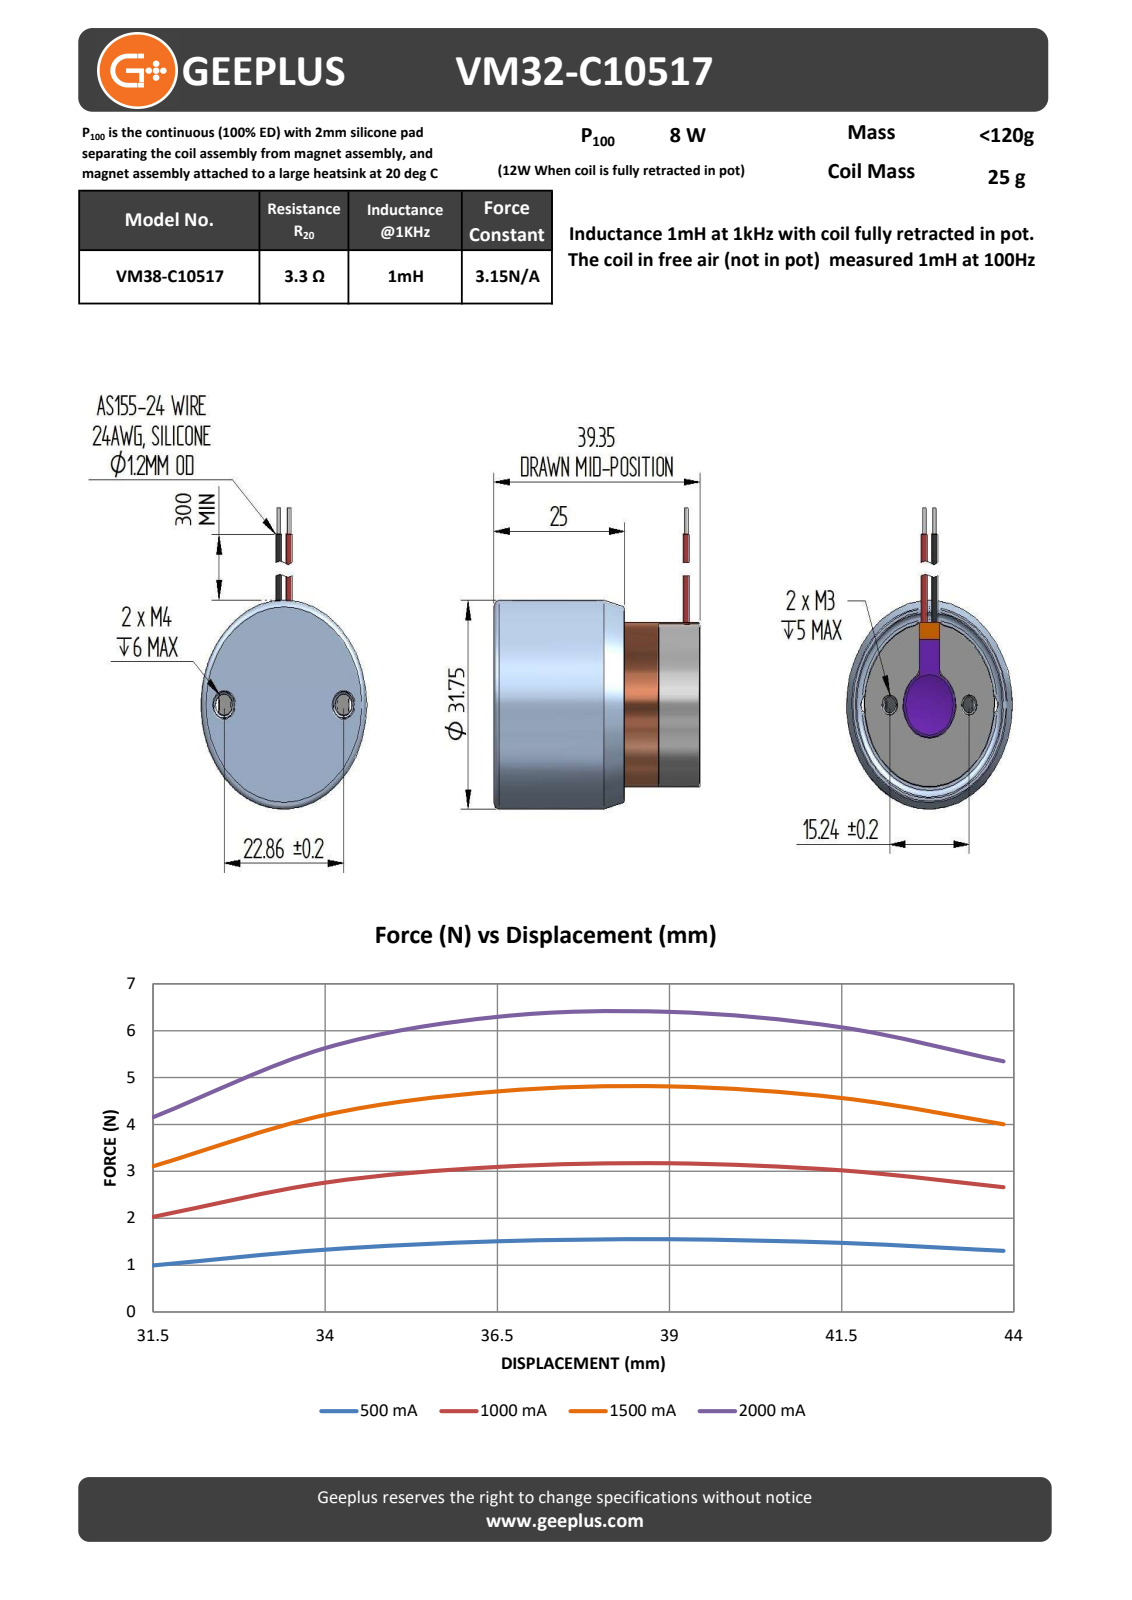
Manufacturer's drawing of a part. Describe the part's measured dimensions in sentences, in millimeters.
The part is named "01-1423; 02-1438; 81-1412; 84-1111 (+8 more)". Its 3-D file was written by "Solid Edge (AUTOMOTIVE_DESIGN)". It is 9 solids with 160 faces: 79 planar, 47 cylindrical and 34 other. Overall it measures 337.28 by 39.35 by 31.75 millimeters. Its volume is 18 259 cubic millimeters and its surface area 17 086 square millimeters. Round holes: 2 of diameter 1, 2 of diameter 2.46, 2 of diameter 3.24, 1 of diameter 10.2, 1 of diameter 11, 1 of diameter 16.1, 1 of diameter 19.4, 1 of diameter 20.4, 1 of diameter 28. Round bosses or shafts: 2 of diameter 0.4, 1 of diameter 31.75, 1 of diameter 25, 1 of diameter 16.6, 1 of diameter 16, 1 of diameter 10, 1 of diameter 7. Partial cylindrical surfaces (rounded edges, fillets, slot ends): 4 of radius 0.5, 3 of radius 1, 2 of radius 1.5, 1 of radius 0.7, 1 of radius 1.6. The main face-to-face distances are 6.5, 15, 10, 25, 9.5, 19.5, 5.5, 21.5, 16, 39.35. The hole center spacings are 3.81, 7.62, 11.43, 19.05, 2, 15.24, 22.86.
